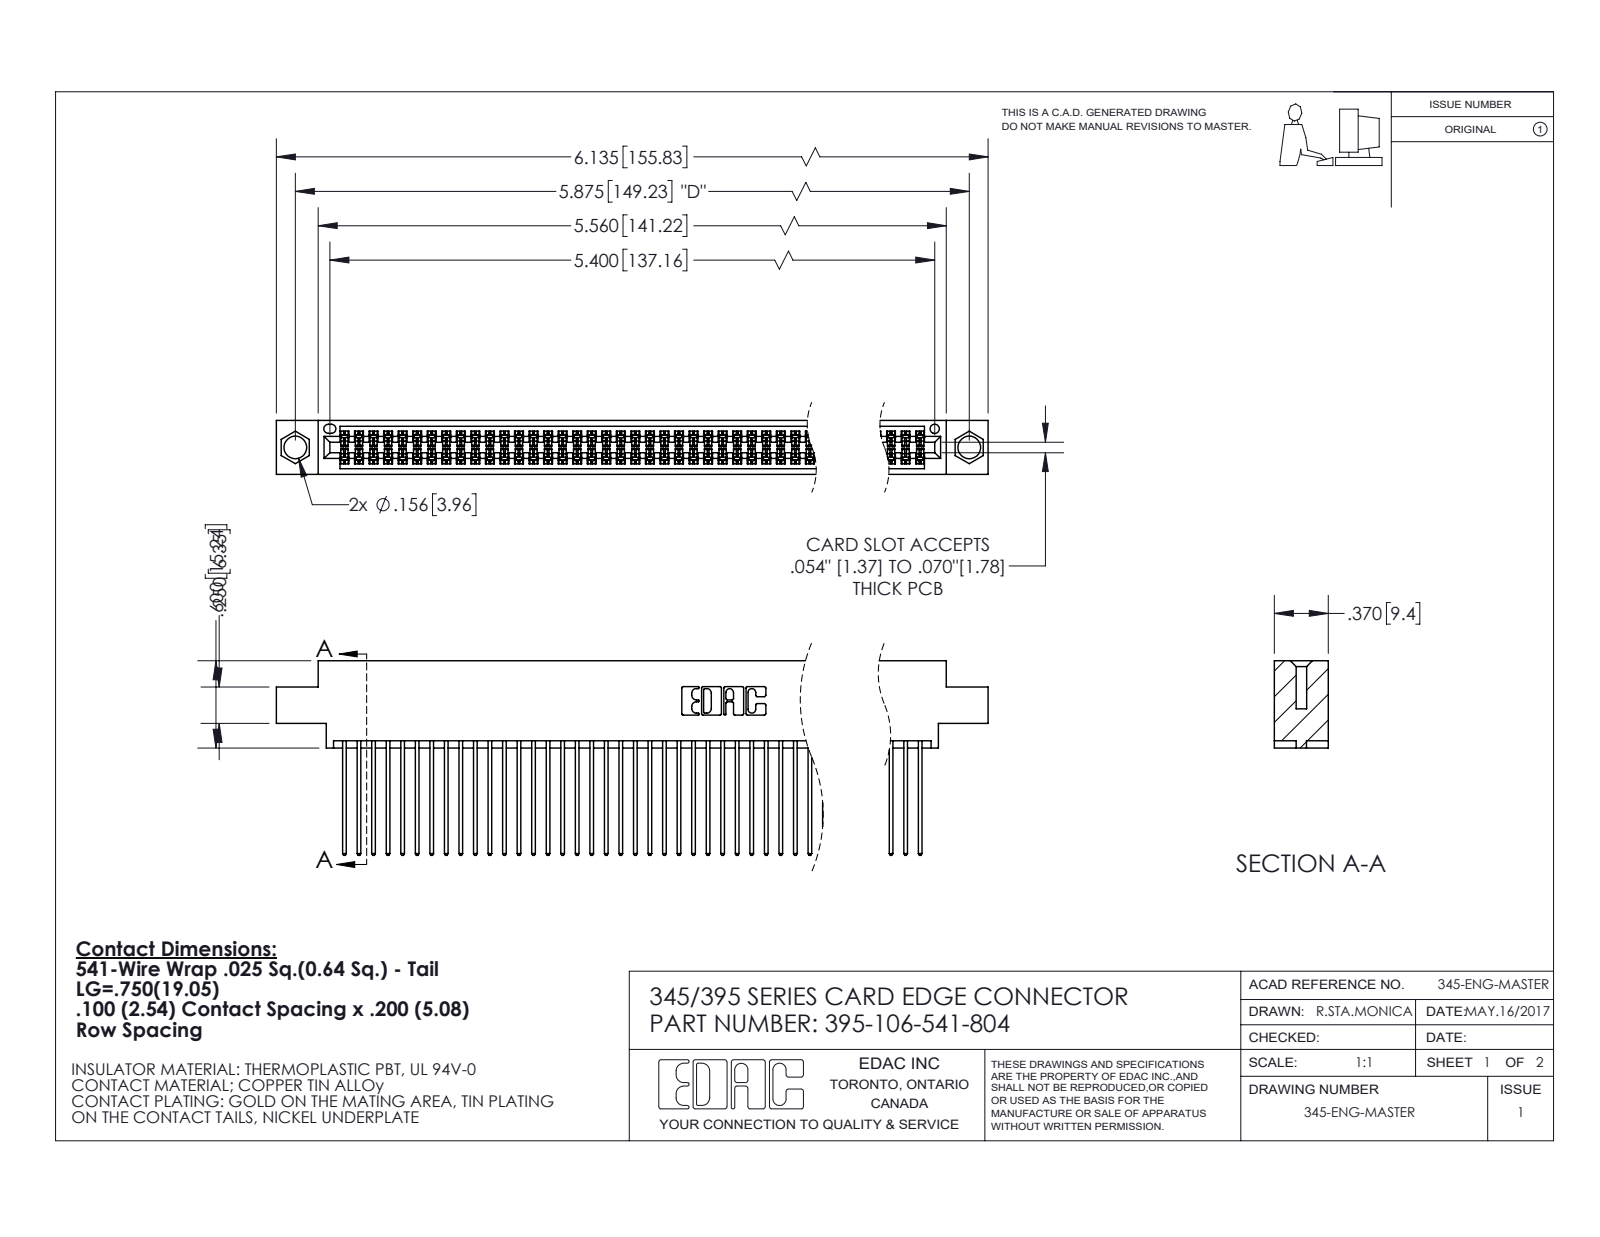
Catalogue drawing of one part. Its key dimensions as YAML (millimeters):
part_name: "345-292-001_345-293-141; 345 Part_0.170 Offset - 0.156 Dia-TI; 395-106-541-804"
step_written_by: "SolidWorks 2020 (CONFIG_CONTROL_DESIGN)"
units: millimeters
bodies: {solids: 107, faces: 5444, planar: 3596, cylindrical: 1848, other: 0}
overall_size: [155.8, 34, 9.4]
volume: 15600
surface_area: 26170
round_holes:
  - {diameter: 4, count: 2}
  - {diameter: 1.6, count: 1}
partial_cylinders:
  - {radius: 0.2, count: 159}
  - {radius: 0.3, count: 106}
  - {radius: 0.3, count: 22}
  - {radius: 0.2, count: 6}
  - {radius: 0.8, count: 6}
  - {radius: 0.7, count: 3}
  - {radius: 0.4, count: 2}
  - {radius: 0.5, count: 2}
face_to_face_distances: [1.8, 7.6, 5.1, 2.5, 6.9, 0.6, 5.7, 9.4, 4.4, 3.8]
hole_center_spacings: [6.9, 143.2, 149.2]
